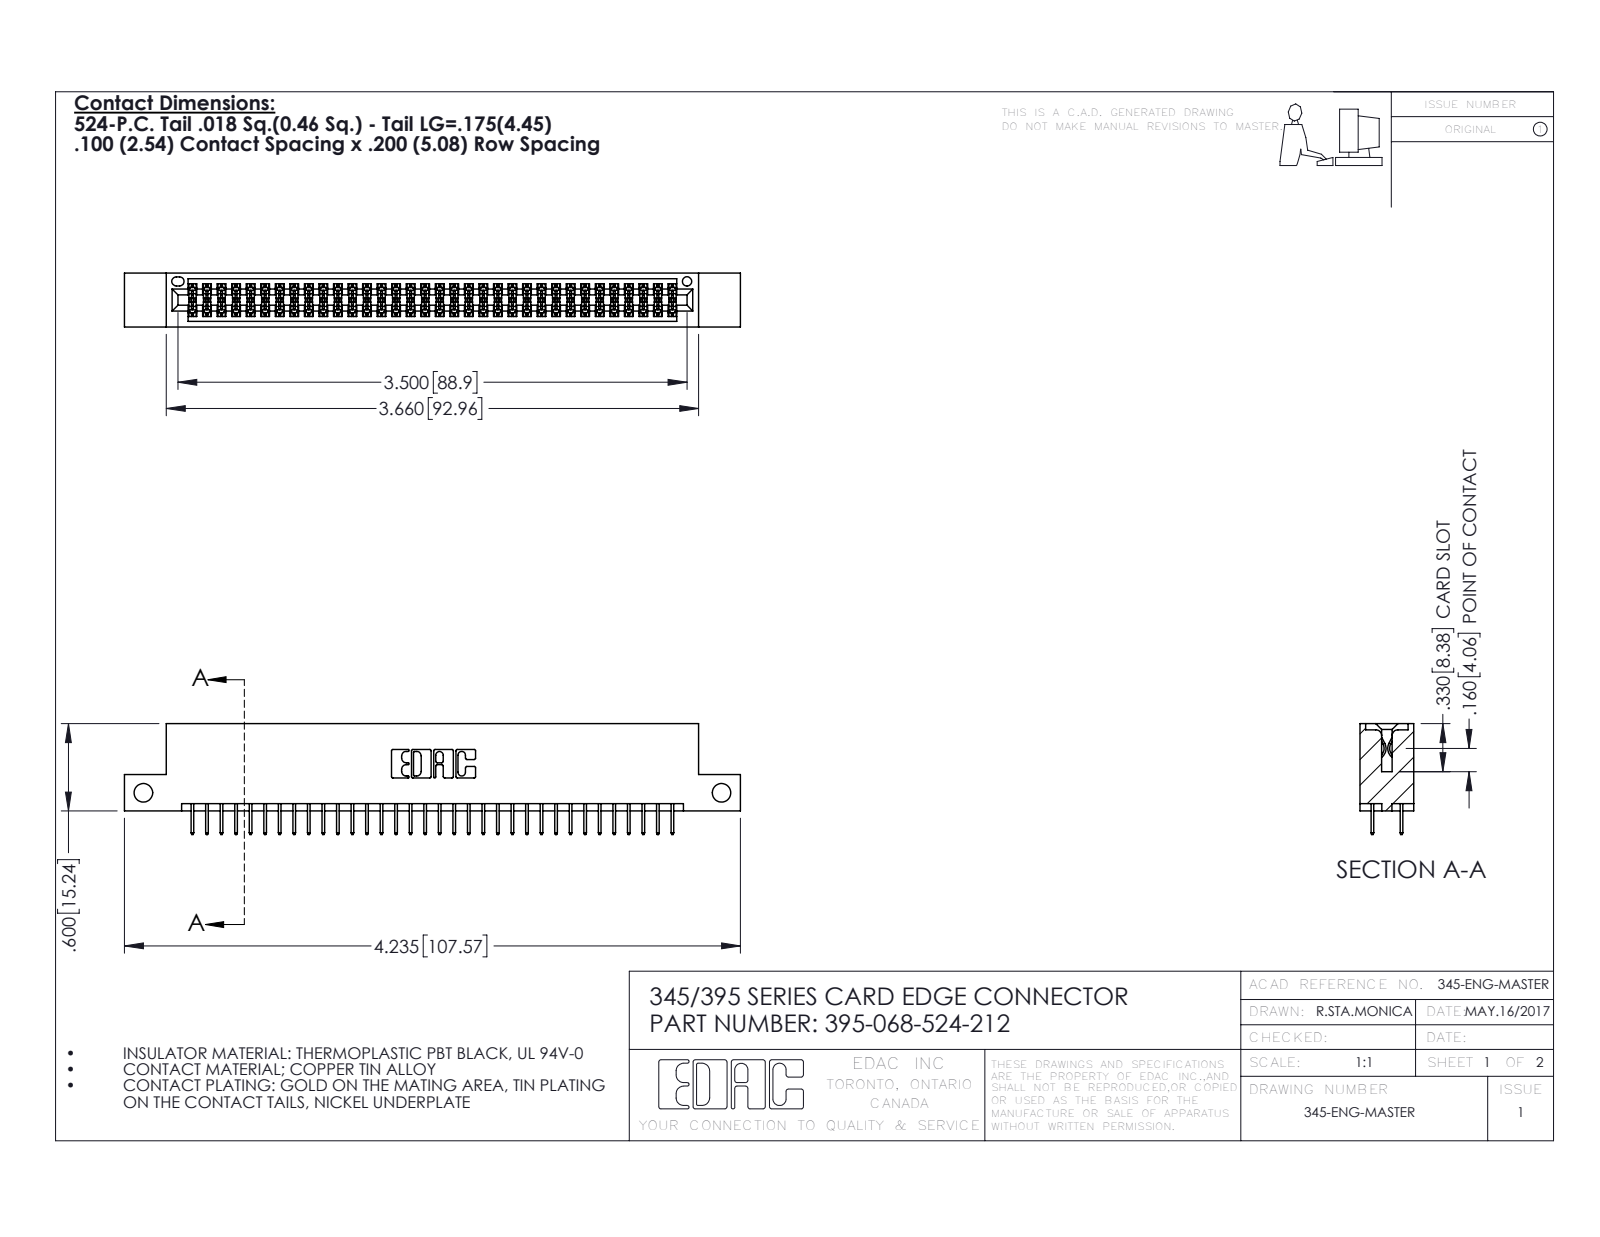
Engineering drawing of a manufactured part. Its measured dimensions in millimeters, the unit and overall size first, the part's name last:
Units: millimetres
Overall size (bounding box): 107.6 × 19.4 × 9.4
Round holes (diameter × count): ⌀3.3 ×2, ⌀1.6 ×1
Partial cylindrical surfaces — rounded edges, fillets, slot ends (radius × count): R0.2 ×102, R0.3 ×22, R0.2 ×6, R0.8 ×6, R0.7 ×3, R0.4 ×2, R0.5 ×2, R0.6 ×2
Main face-to-face distances: 7.6, 1.8, 5.1, 9.4, 2.5, 6.9, 0.6, 5.7, 1.8, 4.4
Hole centre spacings: 101
Volume: 10 200 mm³ · Surface area: 14 490 mm²
Bodies: 69 solids, 3798 faces (2732 planar, 1066 cylindrical, 0 other)
Part name (STEP PRODUCT): 345 Part_Flush Mounting Lugs - Side Mount; 345-292-001_345-293-124; 395-068-524-212
STEP written by: SolidWorks 2016 (CONFIG_CONTROL_DESIGN)
